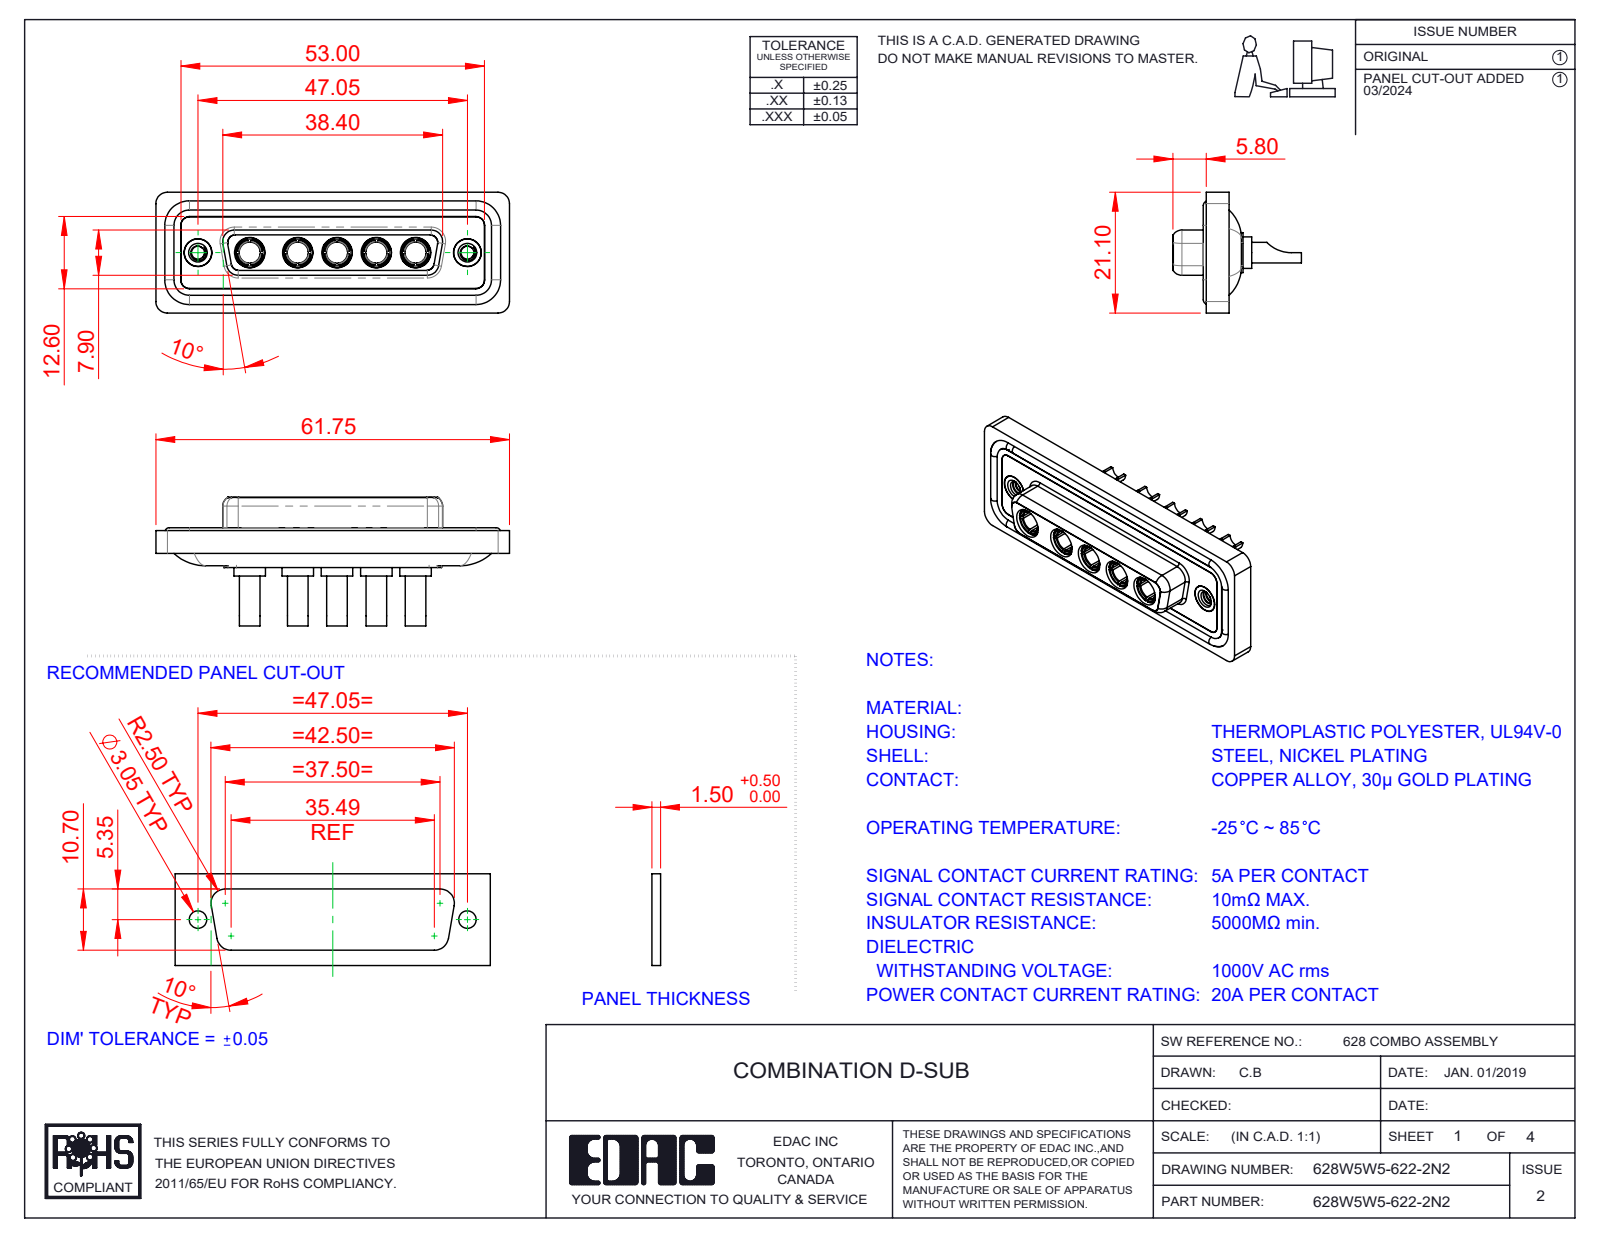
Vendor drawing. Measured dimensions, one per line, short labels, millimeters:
name: 628Combo Waterproof Housing_25 Contacts; 628Combo Shell Front_25 Contacts; 628Combo Threaded Rivet_2; Power Socket_20A SC (+3 more)
written by: SolidWorks 2023 (CONFIG_CONTROL_DESIGN)
unit: mm
bodies: 17 solids, 786 faces (265 planar, 318 cylindrical, 203 other)
size: 61.75 × 22.45 × 21.1
volume: 8 237 mm³; area: 13 828 mm²
holes: 7× ⌀4.85, 5× ⌀2.7, 5× ⌀3.7, 5× ⌀5.3, 2× ⌀2.26, 2× ⌀4, 2× ⌀4.05, 2× ⌀5
bosses: 5× ⌀5.5, 5× ⌀5.2, 5× ⌀4.96, 5× ⌀4.75, 5× ⌀3.75, 5× ⌀3.6, 4× ⌀1.6, 2× ⌀4.95
rounds: 22× R1.5, 18× R2, 8× R1.35, 8× R1.6, 5× R2.1, 4× R0.25, 4× R0.5, 4× R0.6
face distances: 0.4, 1.8, 7.45, 5.65, 0.5, 7.05, 6.6, 1.6, 1.1, 2.9
hole spacings: 6.86, 9.04, 13.72, 38.01, 8.39, 15.25, 15.9, 17.43
